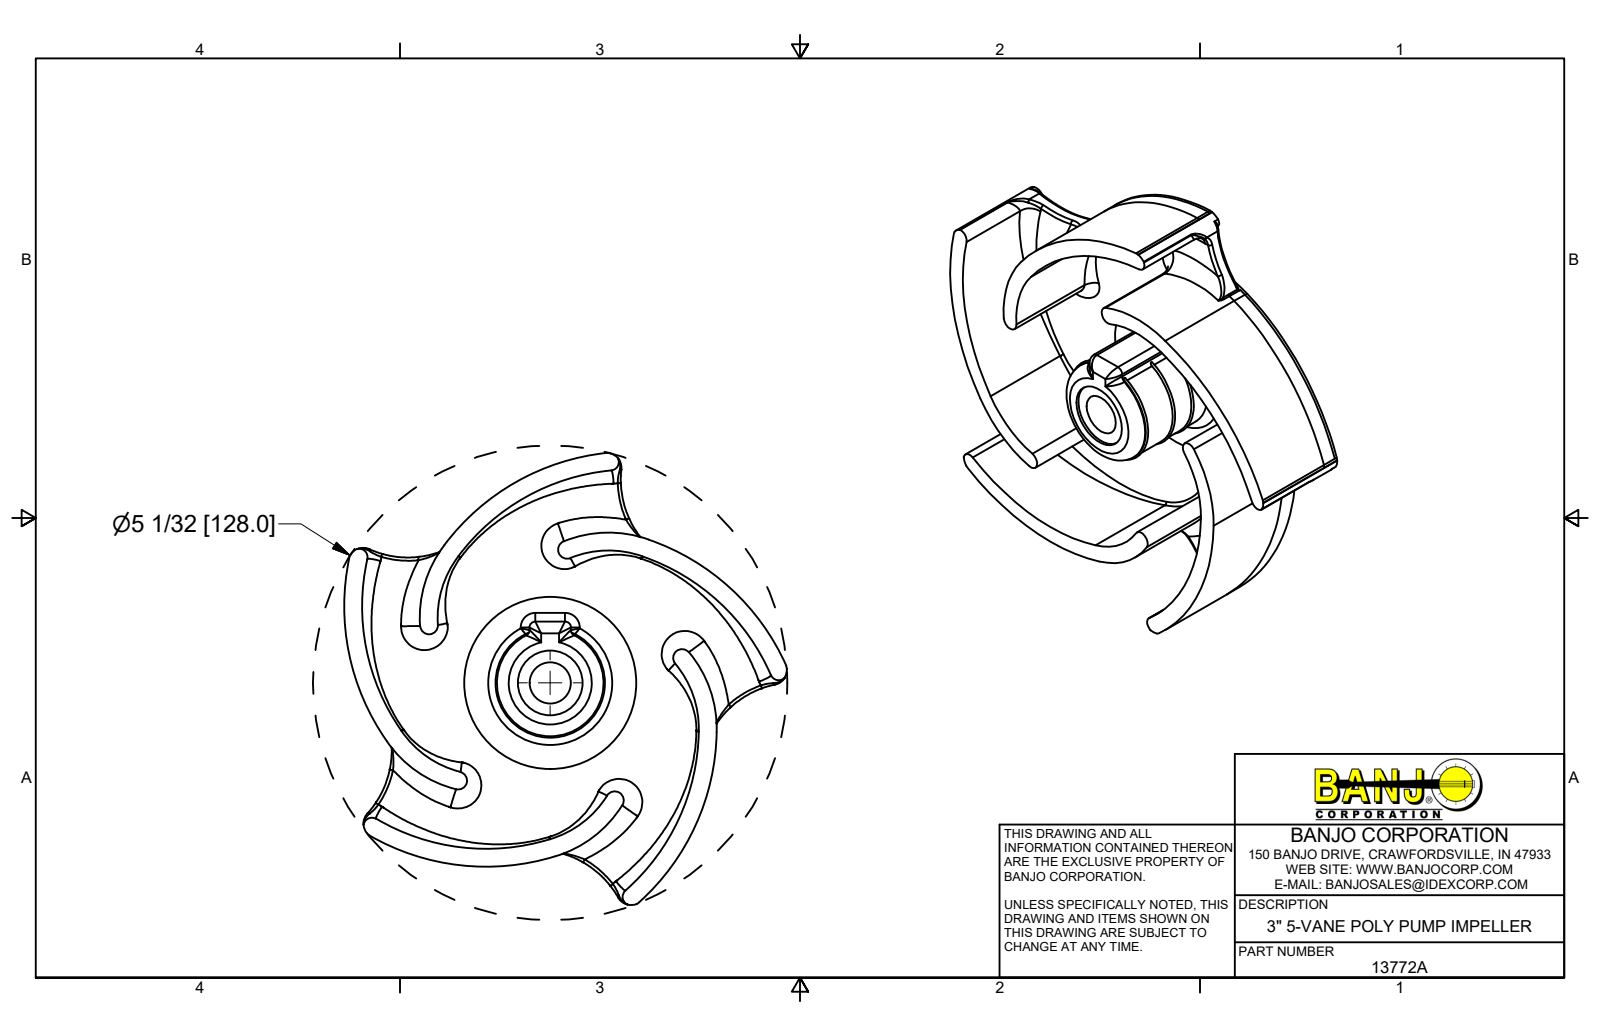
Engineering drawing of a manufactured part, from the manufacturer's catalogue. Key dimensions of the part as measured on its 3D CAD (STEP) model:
Part name (STEP PRODUCT): 13772A
STEP written by: Autodesk Inventor 2018 (AUTOMOTIVE_DESIGN)
Units: inches
Bodies: 1 solid, 528 faces (155 planar, 117 cylindrical, 256 other)
Overall size (bounding box): 4.832 × 4.799 × 1.704
Volume: 6.57 in³ · Surface area: 73.68 in²
Round holes (diameter × count): ⌀0.437 ×1, ⌀0.685 ×1, ⌀0.752 ×1, ⌀1.375 ×1
Round bosses / shafts (diameter × count): ⌀2.73 ×1, ⌀1.75 ×1, ⌀1.13 ×1
Partial cylindrical surfaces — rounded edges, fillets, slot ends (radius × count): R0.015 ×18, R0.031 ×10, R0.09 ×10, R0.095 ×5, R0.16 ×5, R1 ×5, R1.073 ×5, R1.263 ×5
Main face-to-face distances: 1.201, 1.383, 0.182, 1.704, 0.503, 0.321, 0.625, 0.05, 1.151, 1.333
